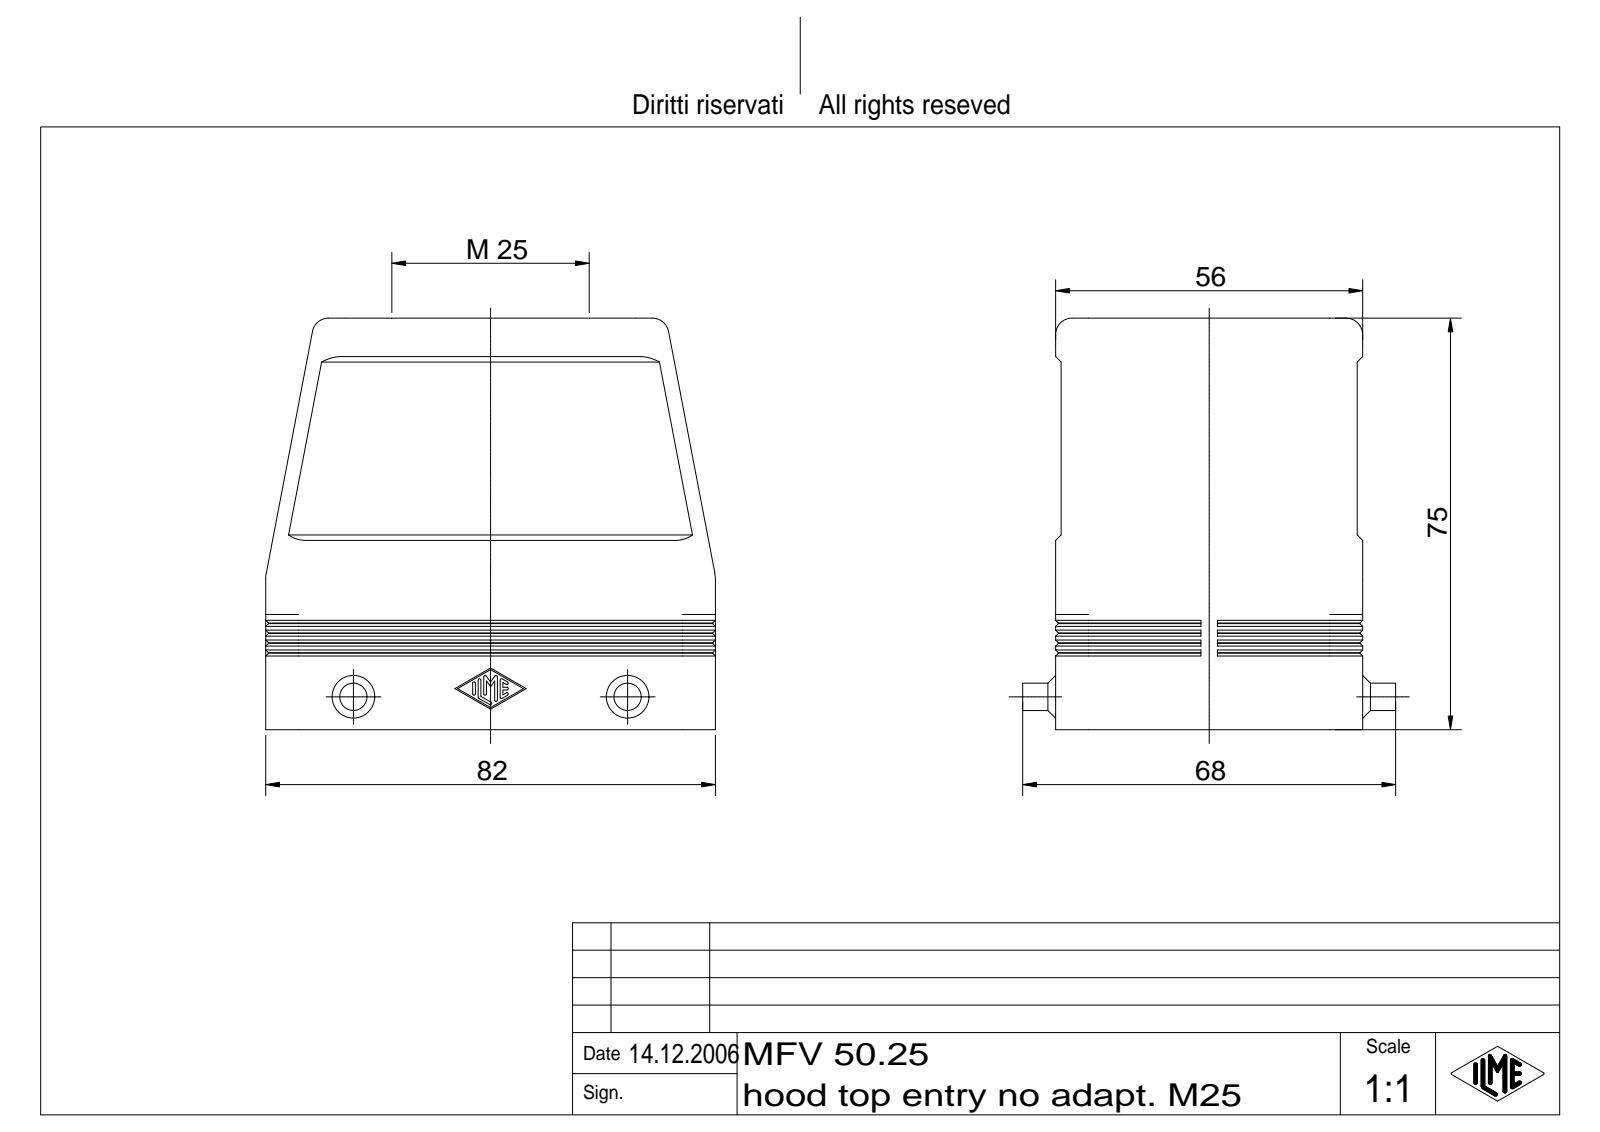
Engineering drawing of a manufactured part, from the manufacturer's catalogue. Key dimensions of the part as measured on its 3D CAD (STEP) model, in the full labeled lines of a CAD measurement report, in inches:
Part name (STEP PRODUCT): MFV 50.25
STEP written by: Autodesk Inventor 7 (AUTOMOTIVE_DESIGN)
Units: inches
Bodies: 1 solid, 443 faces (169 planar, 126 cylindrical, 148 other)
Overall size (bounding box): 3.228 × 2.953 × 2.677
Volume: 4.784 in³ · Surface area: 70.89 in²
Round holes (diameter × count): ⌀0.097 ×4, ⌀0.138 ×4, ⌀1.417 ×1
Round bosses / shafts (diameter × count): ⌀0.197 ×2, ⌀1.811 ×1
Partial cylindrical surfaces — rounded edges, fillets, slot ends (radius × count): R0.01 ×14, R0.236 ×10, R0.079 ×8, R0.118 ×8, R0.217 ×2
Main face-to-face distances: 0.118, 2.087, 1.969, 2.205, 0.079, 0.039, 2.047, 2.165, 0.443, 2.785
Hole centre spacings: 0.63, 1.309, 1.519, 2.598, 2.674
